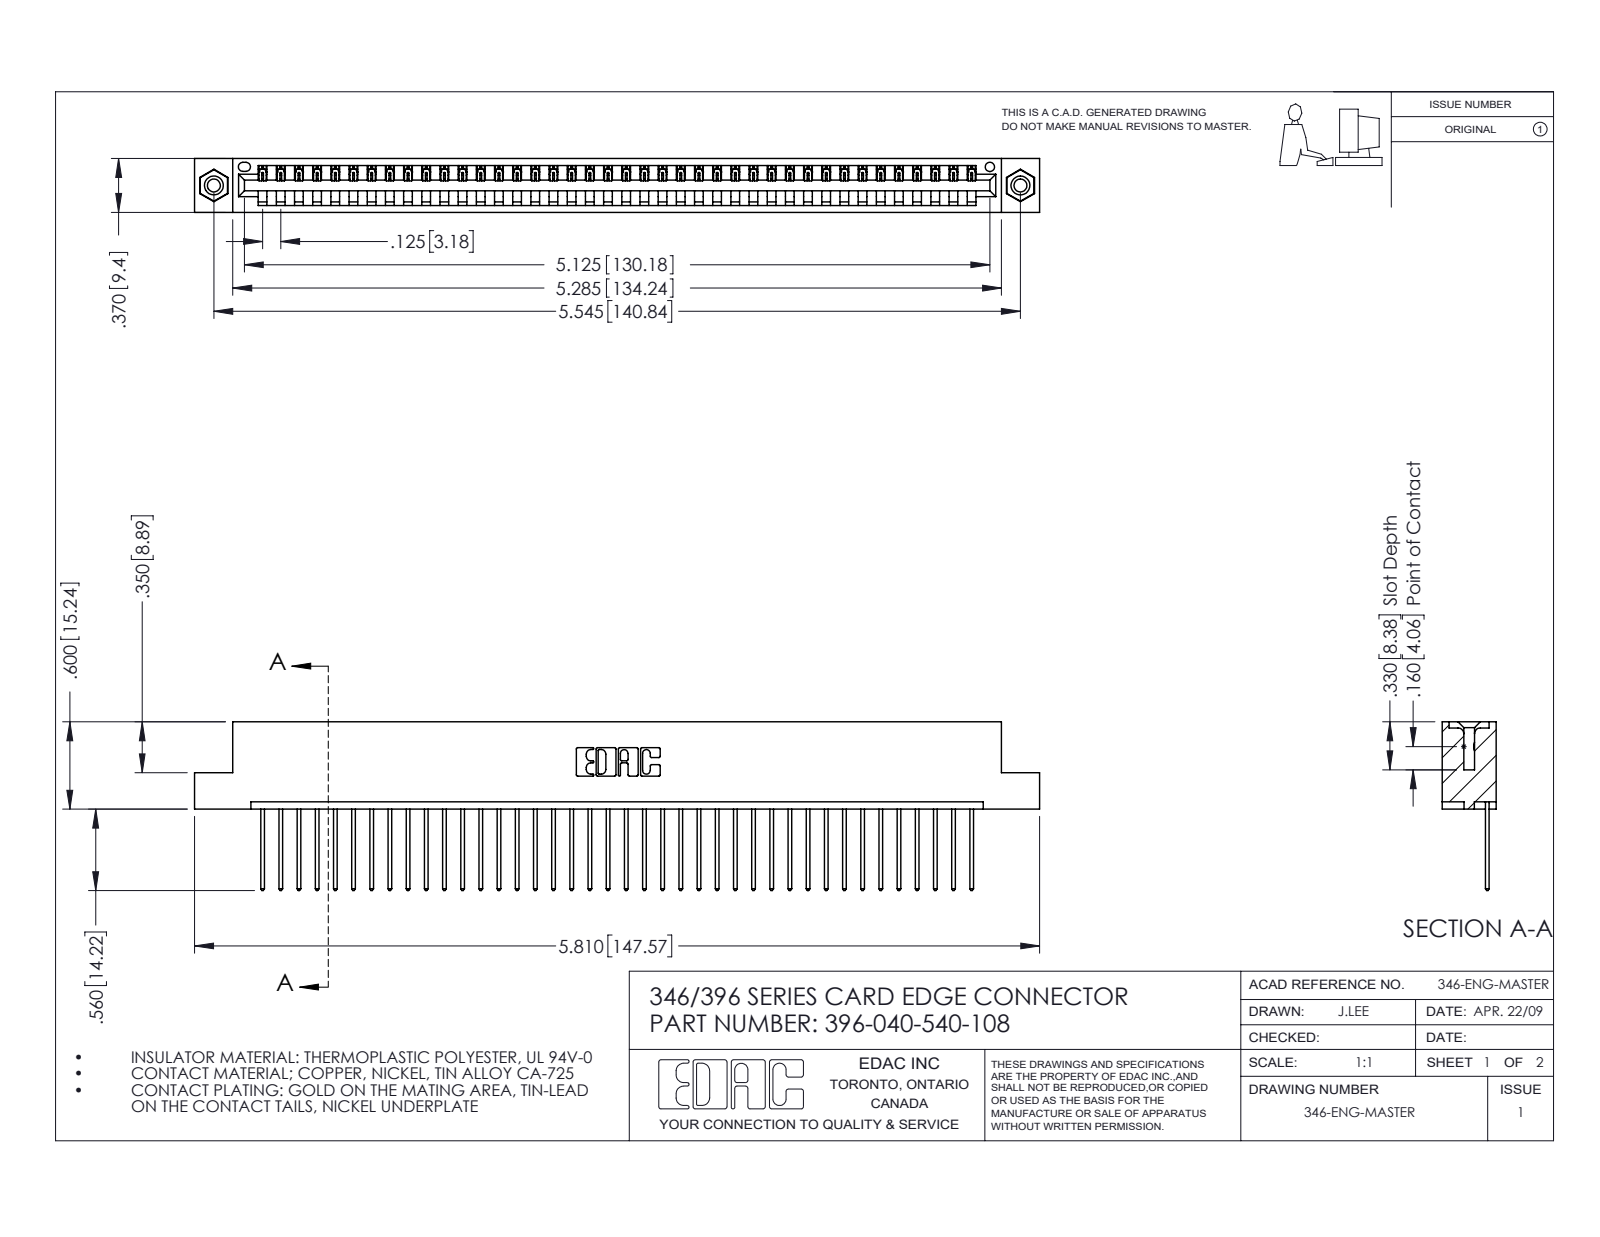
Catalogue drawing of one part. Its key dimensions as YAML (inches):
part_name: "345-292-001_345-293-140; 396-040-540-108; 346 Part_Flush Mounting Lugs - 0.156 Dia-TI; 345-250-001_345-250-003-102"
step_written_by: "SolidWorks 2016 (CONFIG_CONTROL_DESIGN)"
units: inches
bodies: {solids: 43, faces: 2502, planar: 1708, cylindrical: 778, other: 16}
overall_size: [5.81, 1.16, 0.37]
volume: 0.864
surface_area: 28.05
round_holes:
  - {diameter: 0.089, count: 2}
  - {diameter: 0.125, count: 2}
  - {diameter: 0.156, count: 2}
  - {diameter: 0.064, count: 1}
round_bosses_or_shafts:
  - {diameter: 0.155, count: 2}
partial_cylinders:
  - {radius: 0.006, count: 80}
  - {radius: 0.01, count: 80}
  - {radius: 0.01, count: 22}
  - {radius: 0.007, count: 6}
  - {radius: 0.031, count: 6}
  - {radius: 0.026, count: 3}
  - {radius: 0.031, count: 2}
  - {radius: 0.04, count: 2}
face_to_face_distances: [0.048, 0.322, 0.37, 0.25, 0.072, 0.298, 0.025, 0.148, 0.222, 0.1]
hole_center_spacings: [0.246, 5.336, 5.545]
